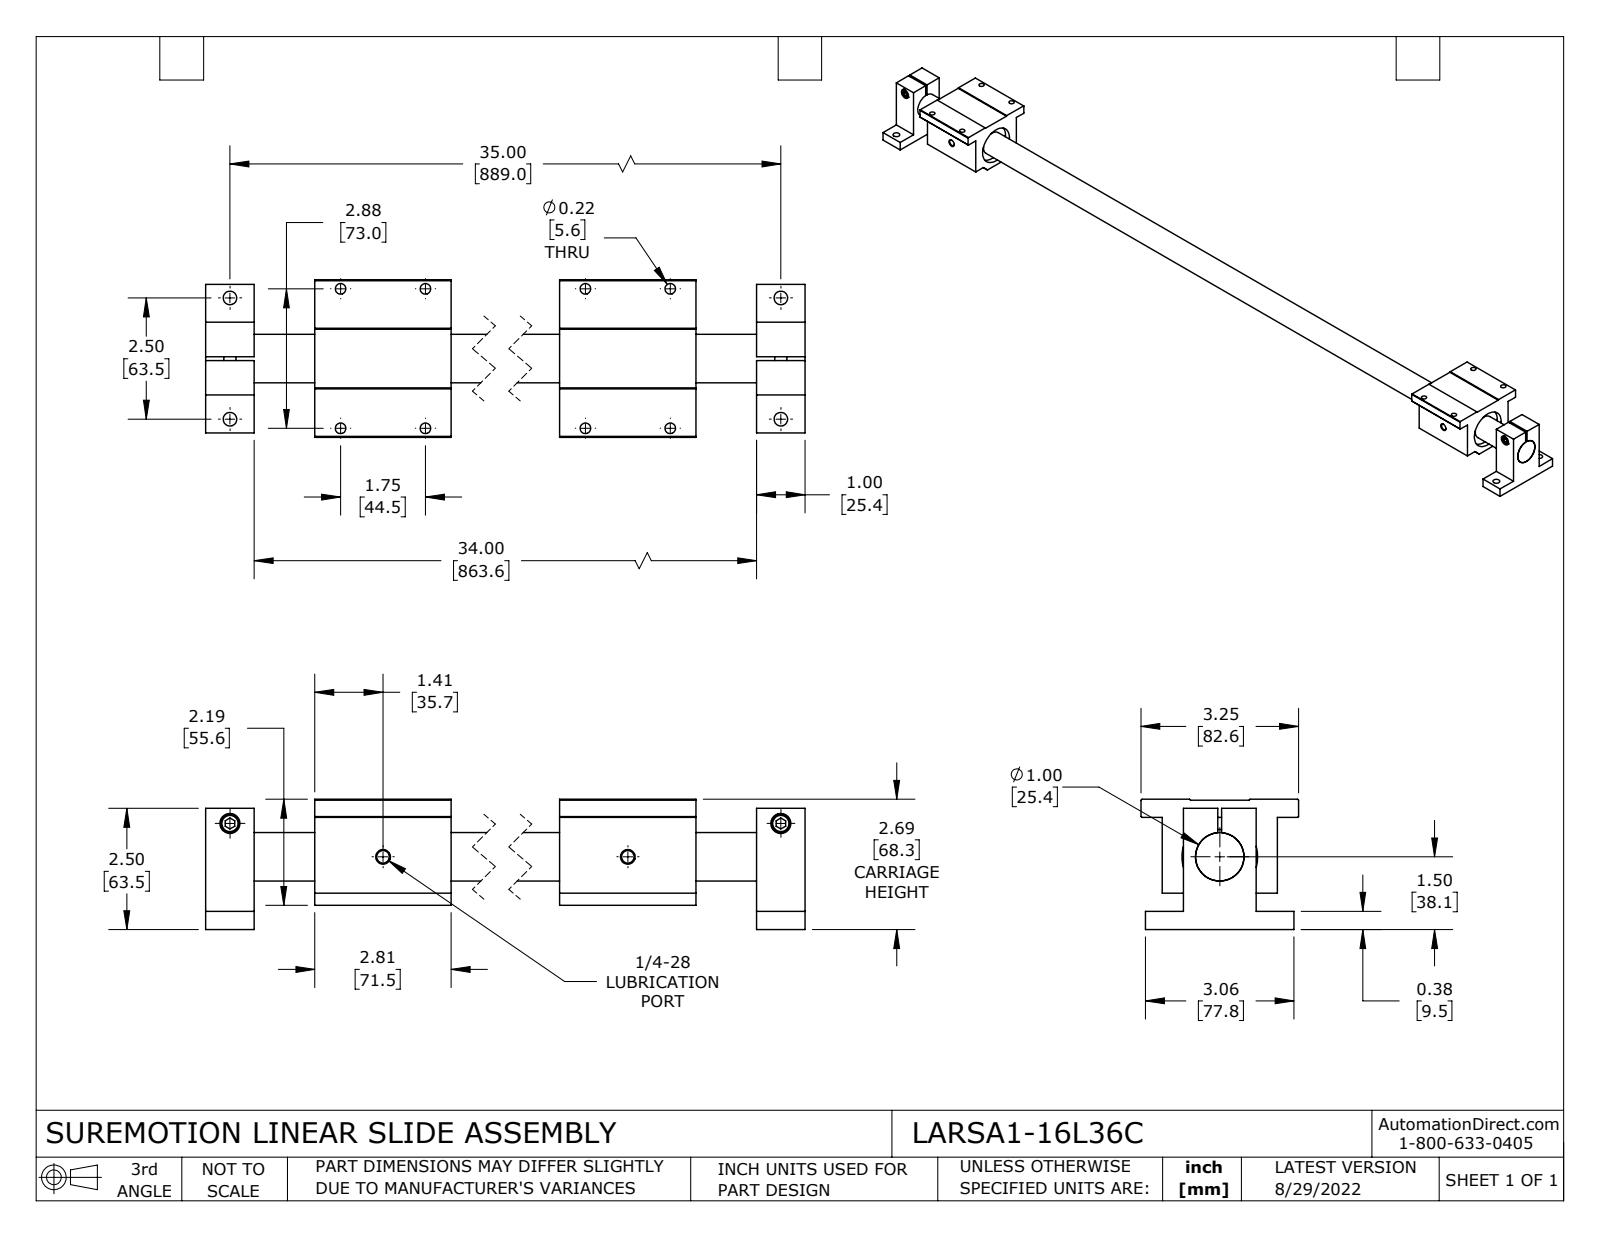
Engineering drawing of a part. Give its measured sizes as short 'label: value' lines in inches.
name: LARSA1-16L36C; LARSA1-16L36C-RAIL; LARSACC-003
written by: SolidWorks 2021 (CONFIG_CONTROL_DESIGN)
unit: in
bodies: 7 solids, 166 faces (98 planar, 60 cylindrical, 8 other)
size: 36 × 3.25 × 2.687
volume: 58.92 in³; area: 260.2 in²
holes: 8× ⌀0.219, 4× ⌀0.281, 2× ⌀0.258, 2× ⌀0.413, 1× ⌀1, 1× ⌀1.563
bosses: 2× ⌀0.375, 2× ⌀0.25
face distances: 2.813, 28.687, 2.376, 0.438, 1.938, 0.375, 2.312, 35, 1, 0.02
hole spacings: 28.687, 1.75, 2.289, 2.875, 3.366, 3.525, 4.036, 4.845
